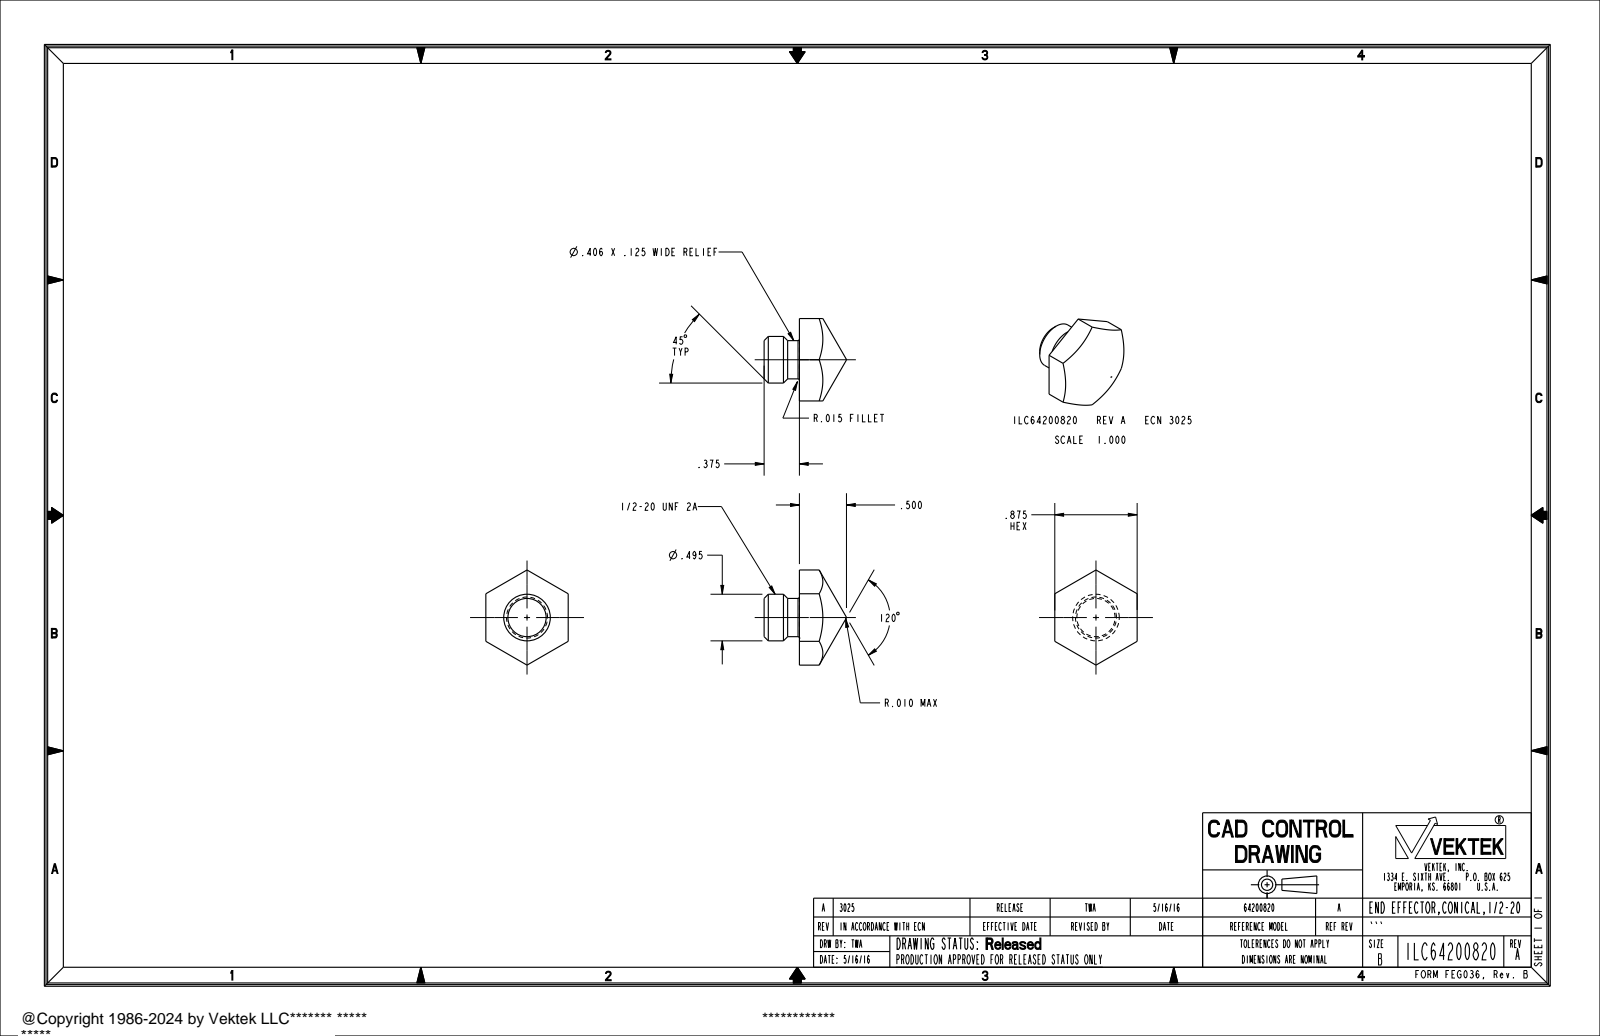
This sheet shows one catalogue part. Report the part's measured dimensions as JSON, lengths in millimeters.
{"part_name": "ILC64200820", "step_written_by": "PRO/ENGINEER BY PARAMETRIC TECHNOLOGY CORPORATION, 2013320 (CONFIG_CONTROL_DESIGN)", "units": "millimeters", "bodies": {"solids": 1, "faces": 22, "planar": 8, "cylindrical": 4, "other": 10}, "overall_size": [25.7, 22.2, 22.2], "volume_mm3": 4520, "surface_area_mm2": 1756, "round_bosses_or_shafts": [[12.6, 1], [10.3, 1]], "face_to_face_distances": [22.2, 9.5]}
